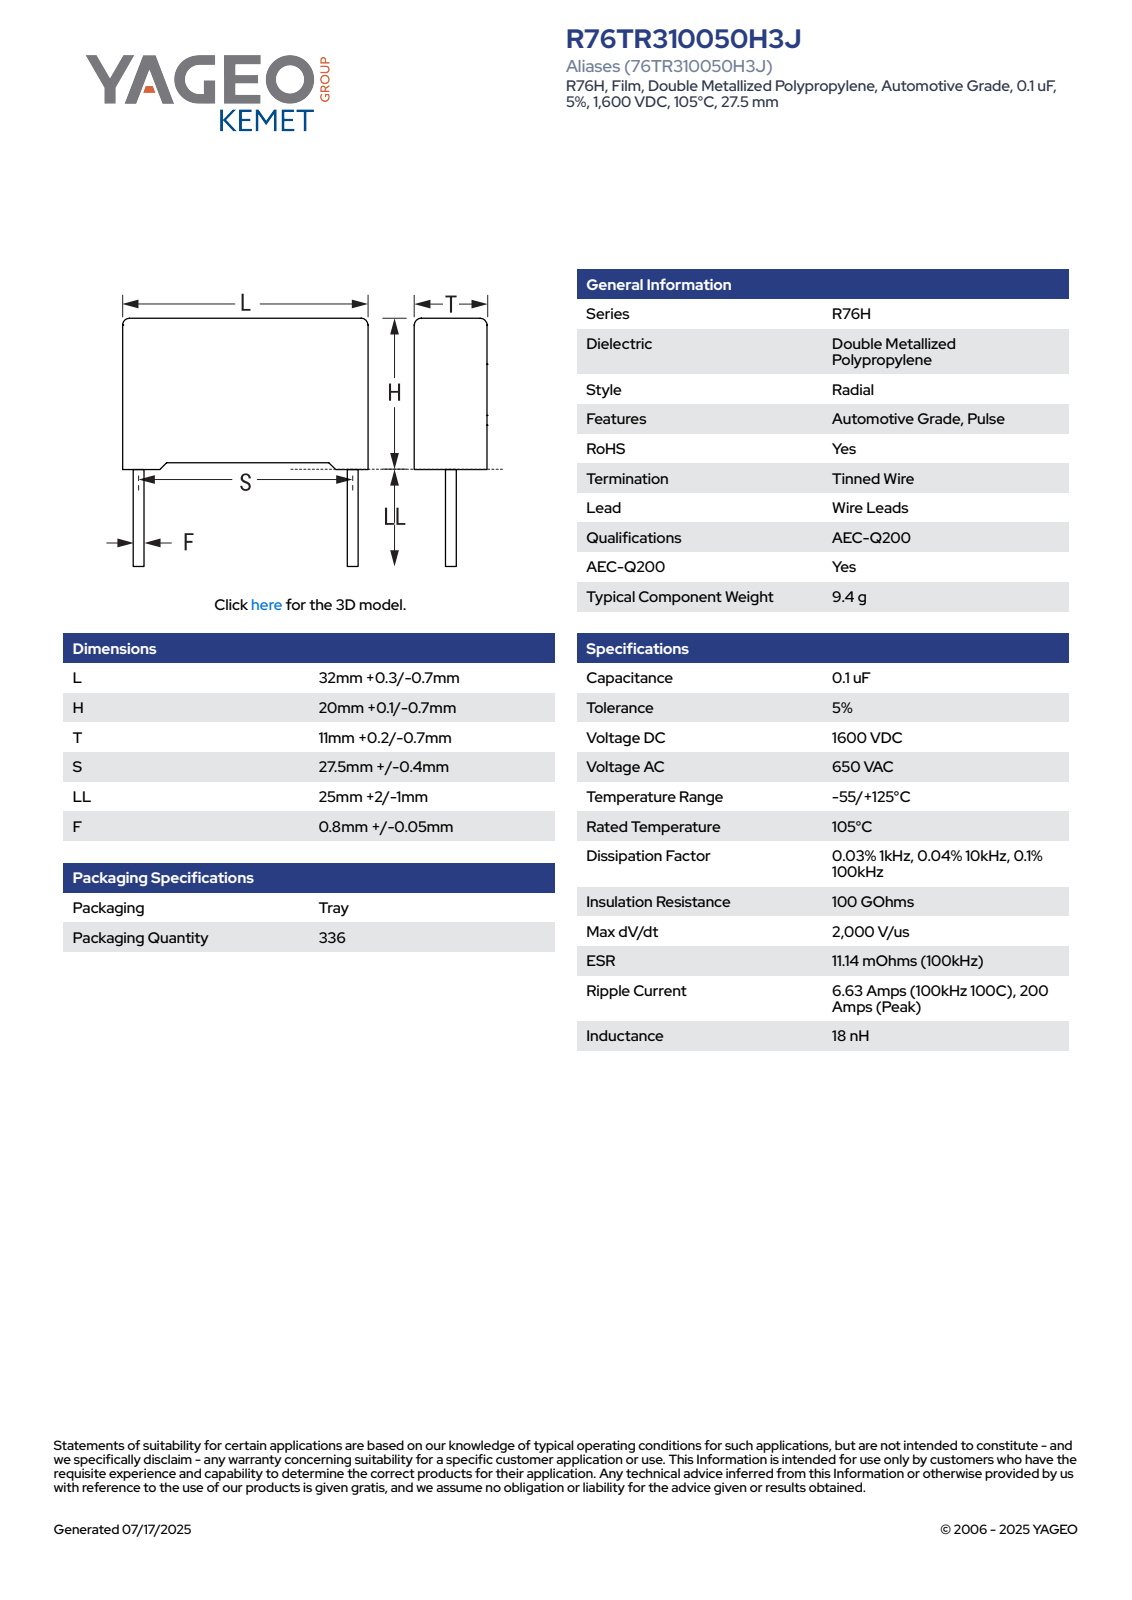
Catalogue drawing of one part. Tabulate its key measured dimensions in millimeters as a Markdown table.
| quantity | value |
| --- | --- |
| part name | CFR_RB2R76_32X20X11_L32.3H20.1T11.2S27.5LL27F0.85 |
| STEP written by | SolidWorks 2014 (AUTOMOTIVE_DESIGN) |
| units | millimeters |
| bodies | 4 solids, 85 faces (77 planar, 8 cylindrical, 0 other) |
| overall size | 47.1 × 32.3 × 11.21 |
| volume | 7 059 mm³ |
| surface area | 2 674 mm² |
| round bosses / shafts (diameter × count) | 0.85 × 2 |
| partial cylindrical surfaces (radius × count) | 0.5 × 4 |
| main face-to-face distances | 11.2, 19.35, 32.3, 19.41, 0.69, 0.75, 20.1, 1.08, 11.21, 31.22 |
